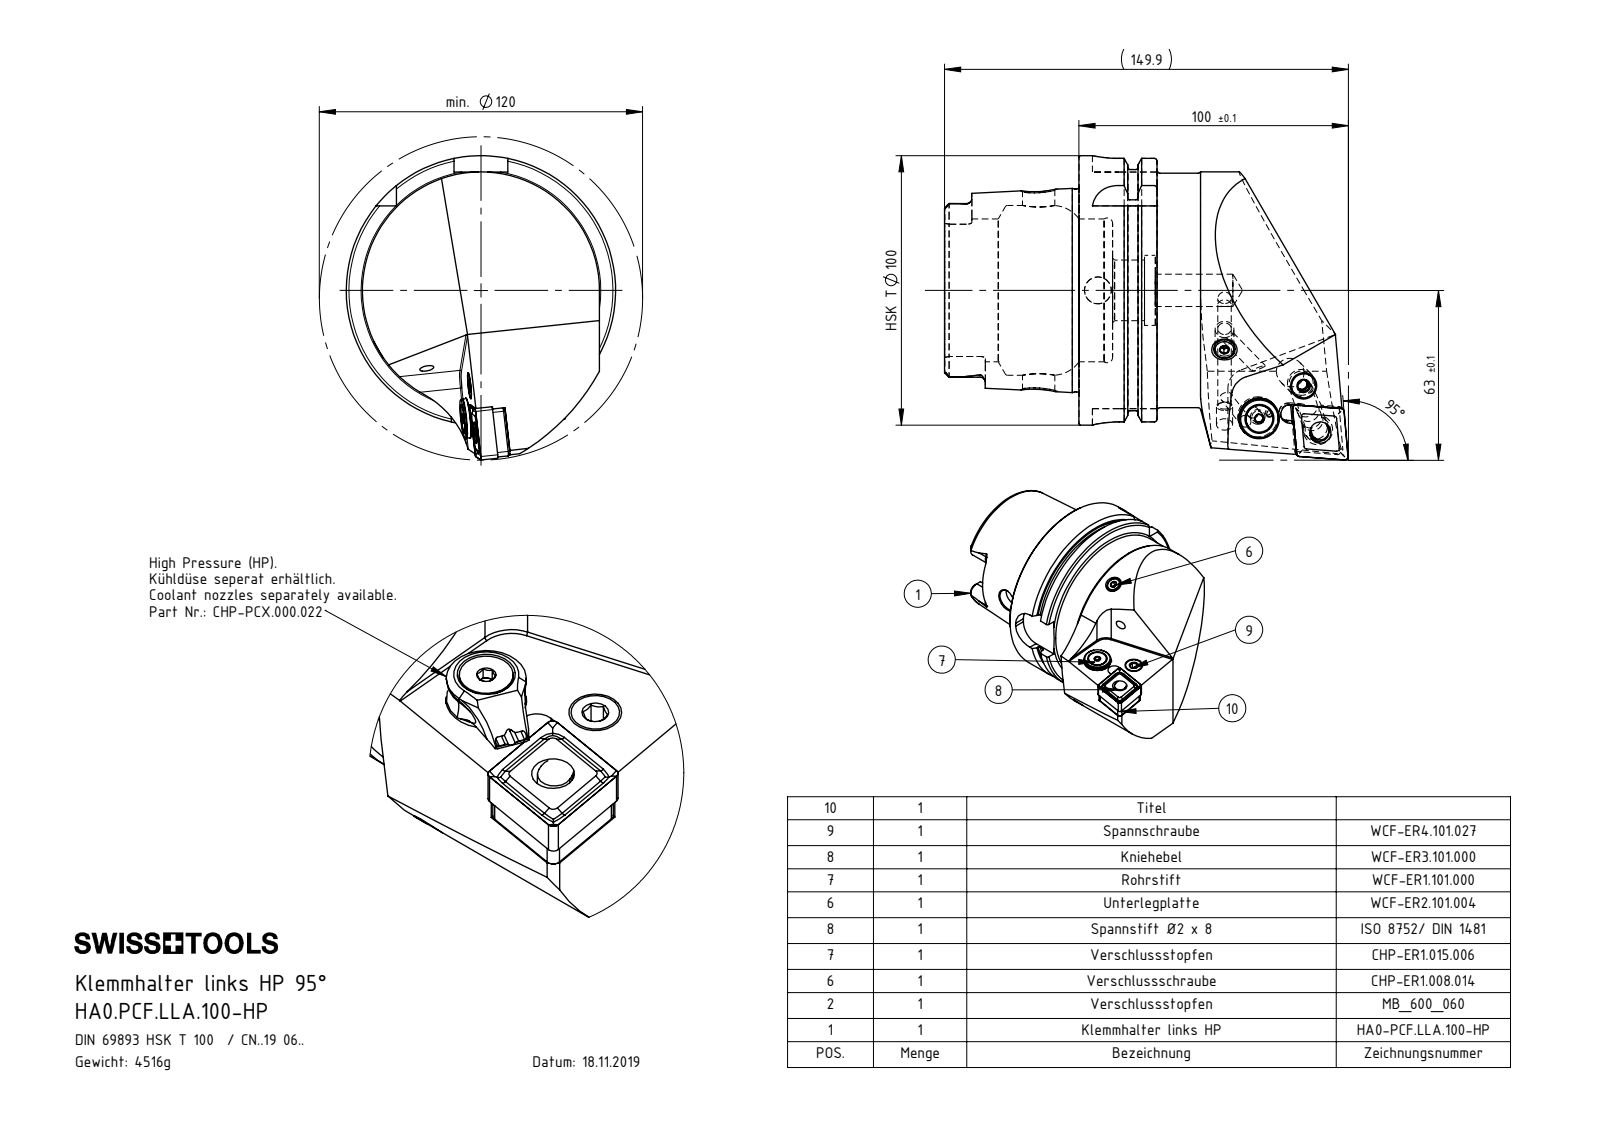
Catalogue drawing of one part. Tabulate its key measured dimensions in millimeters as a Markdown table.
| quantity | value |
| --- | --- |
| part name | WCF-ER4.101.027_A; HA0-PCF.LLA.100-HP_A_Fertigbearbeitung; CHP-ER1.008.014_A; CHP-ER1.015.006_A (+8 more) |
| STEP written by | SolidWorks 2022 (CONFIG_CONTROL_DESIGN) |
| units | millimeters |
| bodies | 13 solids, 531 faces (165 planar, 144 cylindrical, 222 other) |
| overall size | 149.81 × 112.92 × 100 |
| volume | 573 960 mm³ |
| surface area | 78 539 mm² |
| round holes (diameter × count) | 5 × 3, 4.2 × 2, 12 × 2, 1.2 × 1, 2 × 1, 2.5 × 1, 3 × 1, 4 × 1, 5.2 × 1, 7 × 1, 7.94 × 1, 9 × 1 |
| round bosses / shafts (diameter × count) | 10 × 2, 100 × 1, 91.95 × 1, 87 × 1, 75.26 × 1, 15 × 1, 13.4 × 1, 9.9 × 1 |
| partial cylindrical surfaces (radius × count) | 1.9 × 6, 1.2 × 4, 1.5 × 4, 10 × 4, 4 × 3, 0.5 × 2, 4.7 × 2, 4.83 × 2 |
| main face-to-face distances | 12.45, 28.95, 16.5, 49.9, 62.35, 78.85, 6.05, 87.8, 0.65, 78.2 |
| hole center spacings | 4.5, 16.43, 20.51, 2.24, 16.05, 18.8, 19.69, 19.96 |
